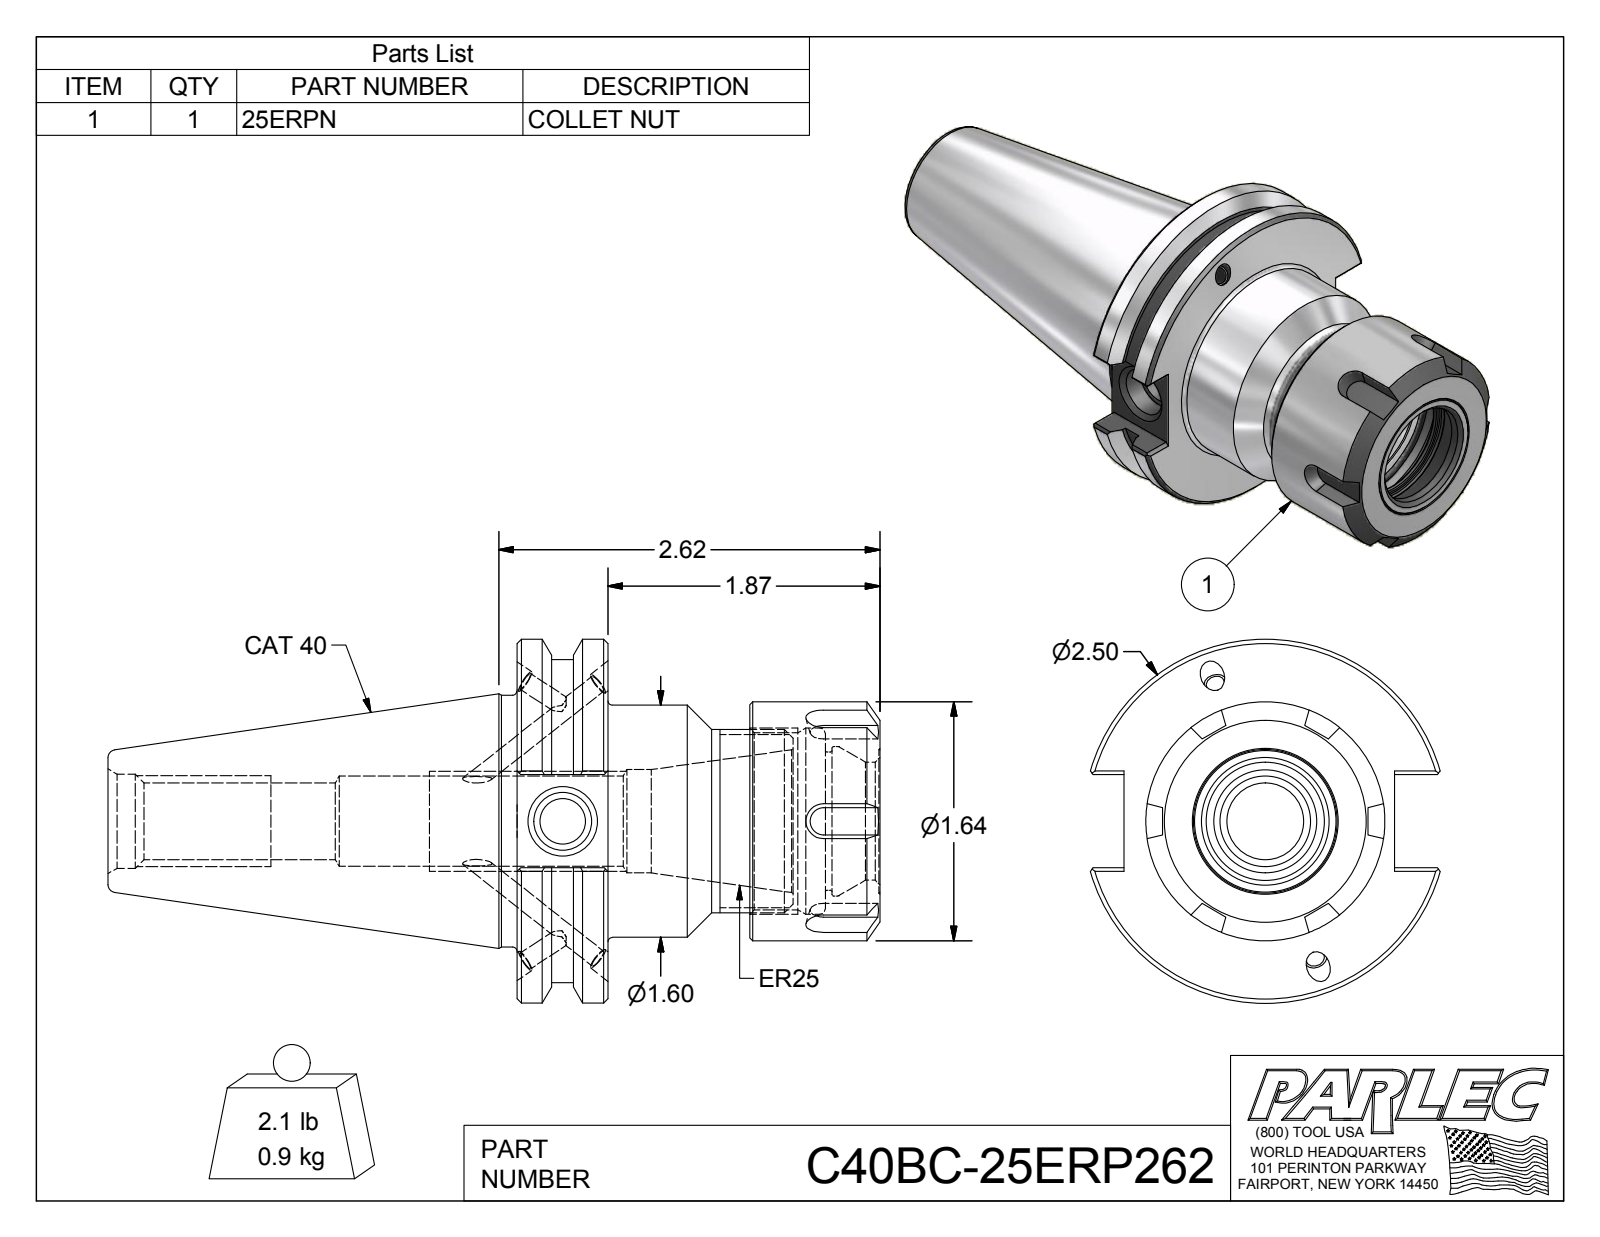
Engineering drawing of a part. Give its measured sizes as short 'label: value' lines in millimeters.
name: 25ERPN; C40BC-25ER2-1; 029-965; C40BC-25ERP262
written by: Autodesk Inventor 2016 (AUTOMOTIVE_DESIGN)
unit: mm
bodies: 6 solids, 197 faces (98 planar, 41 cylindrical, 58 other)
size: 134.81 × 63.5 × 61.05
volume: 135 488 mm³; area: 33 827 mm²
holes: 4× ⌀3.3, 4× ⌀4.1, 1× ⌀8, 1× ⌀10.05, 1× ⌀13.39, 1× ⌀15.75, 1× ⌀16.46, 1× ⌀18.03, 1× ⌀20.6, 1× ⌀24.13, 1× ⌀26.09, 1× ⌀30.91
bosses: 4× ⌀4.2, 4× ⌀4, 1× ⌀63.5, 1× ⌀56.36, 1× ⌀43.94, 1× ⌀41.73, 1× ⌀40.51, 1× ⌀32
face distances: 15.88, 63.38, 47.5, 40.7, 24.82, 22.68, 53.85, 37.97, 13.15, 9.53
